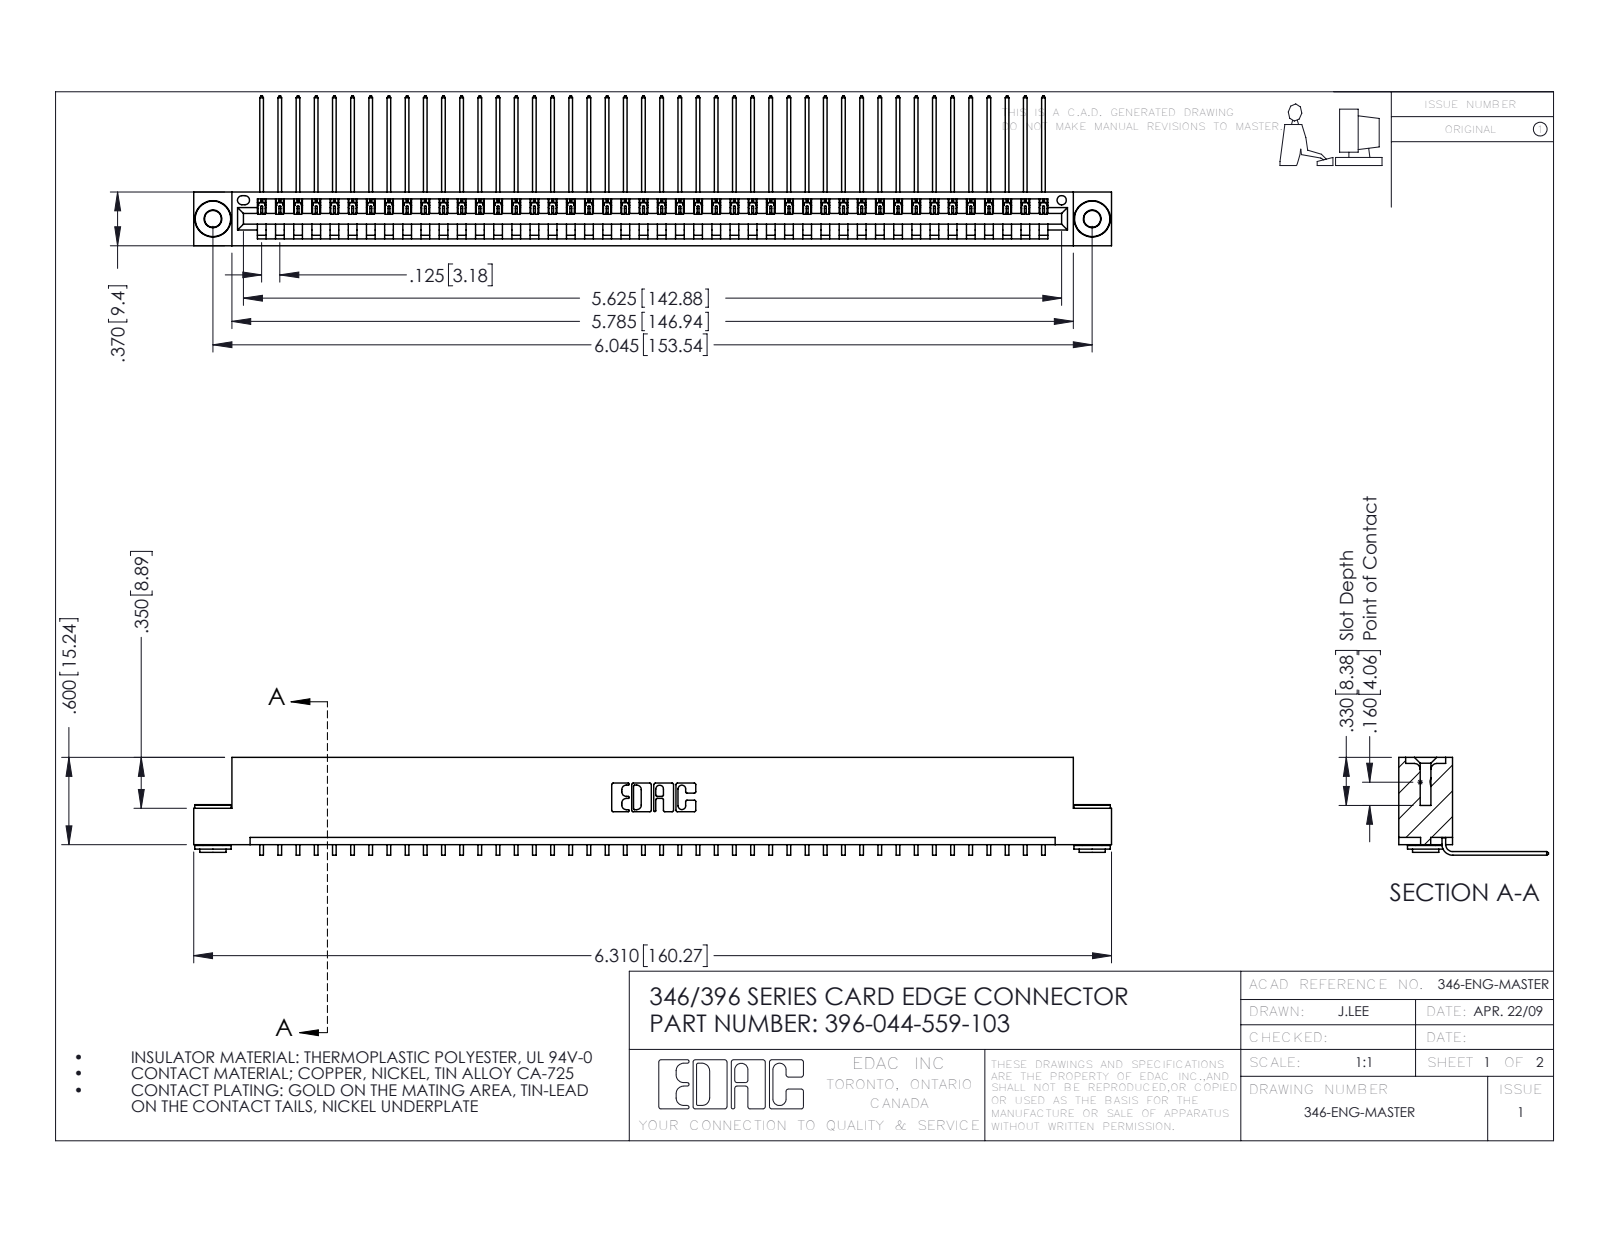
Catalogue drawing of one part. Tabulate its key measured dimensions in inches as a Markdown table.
| quantity | value |
| --- | --- |
| part name | 345-250-002_345-250-002-102; 345-292-001_558 559 Tail - 1; 396-044-559-103; 346 Part_Flush Mounting Lugs - 0.156 Dia-TH |
| STEP written by | SolidWorks 2016 (CONFIG_CONTROL_DESIGN) |
| units | inches |
| bodies | 47 solids, 2800 faces (1934 planar, 858 cylindrical, 8 other) |
| overall size | 6.31 × 1.03 × 0.673 |
| volume | 0.947 in³ |
| surface area | 31.8 in² |
| round holes (diameter × count) | 0.116 × 2, 0.156 × 2, 0.064 × 1 |
| round bosses / shafts (diameter × count) | 0.25 × 2, 0.18 × 2, 0.136 × 2 |
| partial cylindrical surfaces (radius × count) | 0.006 × 88, 0.01 × 22, 0.007 × 6, 0.031 × 6, 0.026 × 3, 0.031 × 2, 0.04 × 2, 0.014 × 1 |
| main face-to-face distances | 0.048, 0.322, 0.37, 0.25, 0.025, 0.072, 0.298, 0.148, 0.222, 0.1 |
| hole center spacings | 0.246, 5.836, 6.045 |
